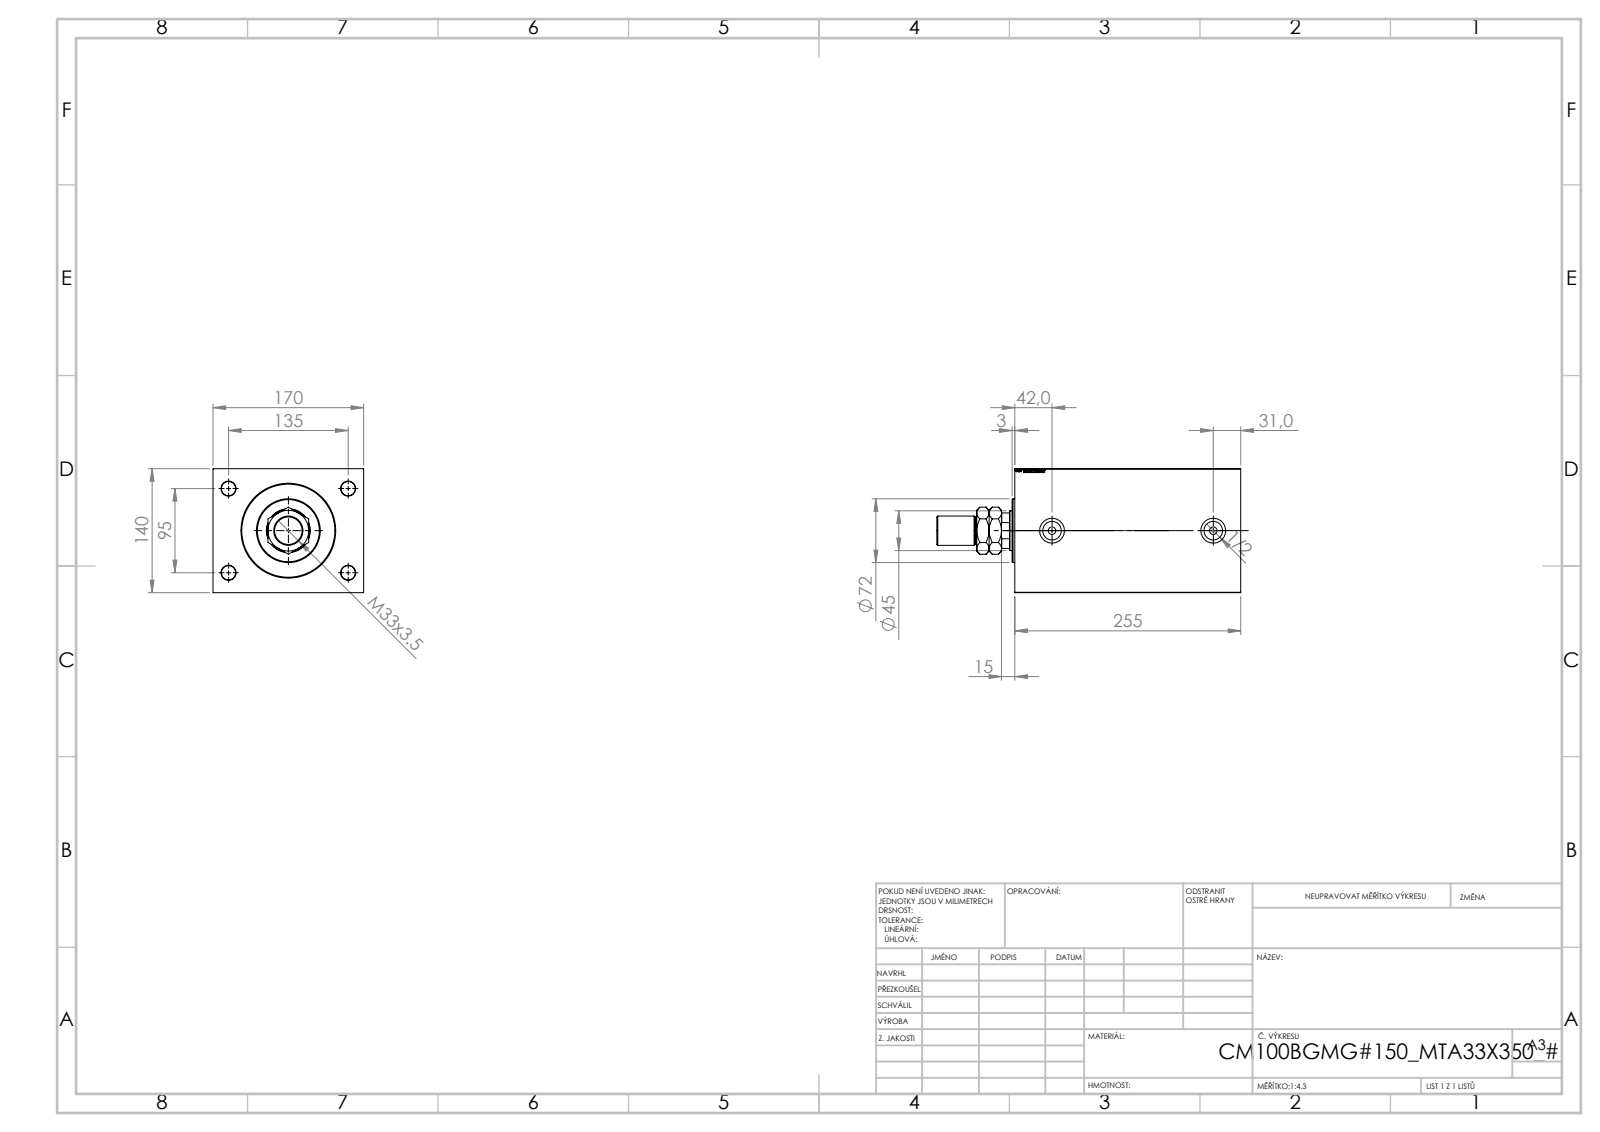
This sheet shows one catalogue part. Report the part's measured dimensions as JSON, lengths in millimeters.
{"part_name": "V450CM_B_VCP; V450CM_B_Body; MTA; V450CM_VC_B", "step_written_by": "SolidWorks 2019 (CONFIG_CONTROL_DESIGN)", "units": "millimeters", "bodies": {"solids": 4, "faces": 933, "planar": 417, "cylindrical": 60, "other": 456}, "overall_size": [343, 170, 140], "volume_mm3": 5153000, "surface_area_mm2": 392141, "round_holes": [[16, 4], [8.5, 2], [20.96, 2], [28, 2], [31.5, 1], [45, 1], [48.5, 1], [49.5, 1], [100, 1], [102, 1], [105, 1]], "round_bosses_or_shafts": [[72, 1], [33, 1], [31, 1]], "partial_cylinders_radius": [[22, 1]], "face_to_face_distances": [140, 170, 255, 229, 26, 15, 214, 240, 90, 64], "hole_center_spacings": [82.54, 95, 135, 165.08, 182]}
